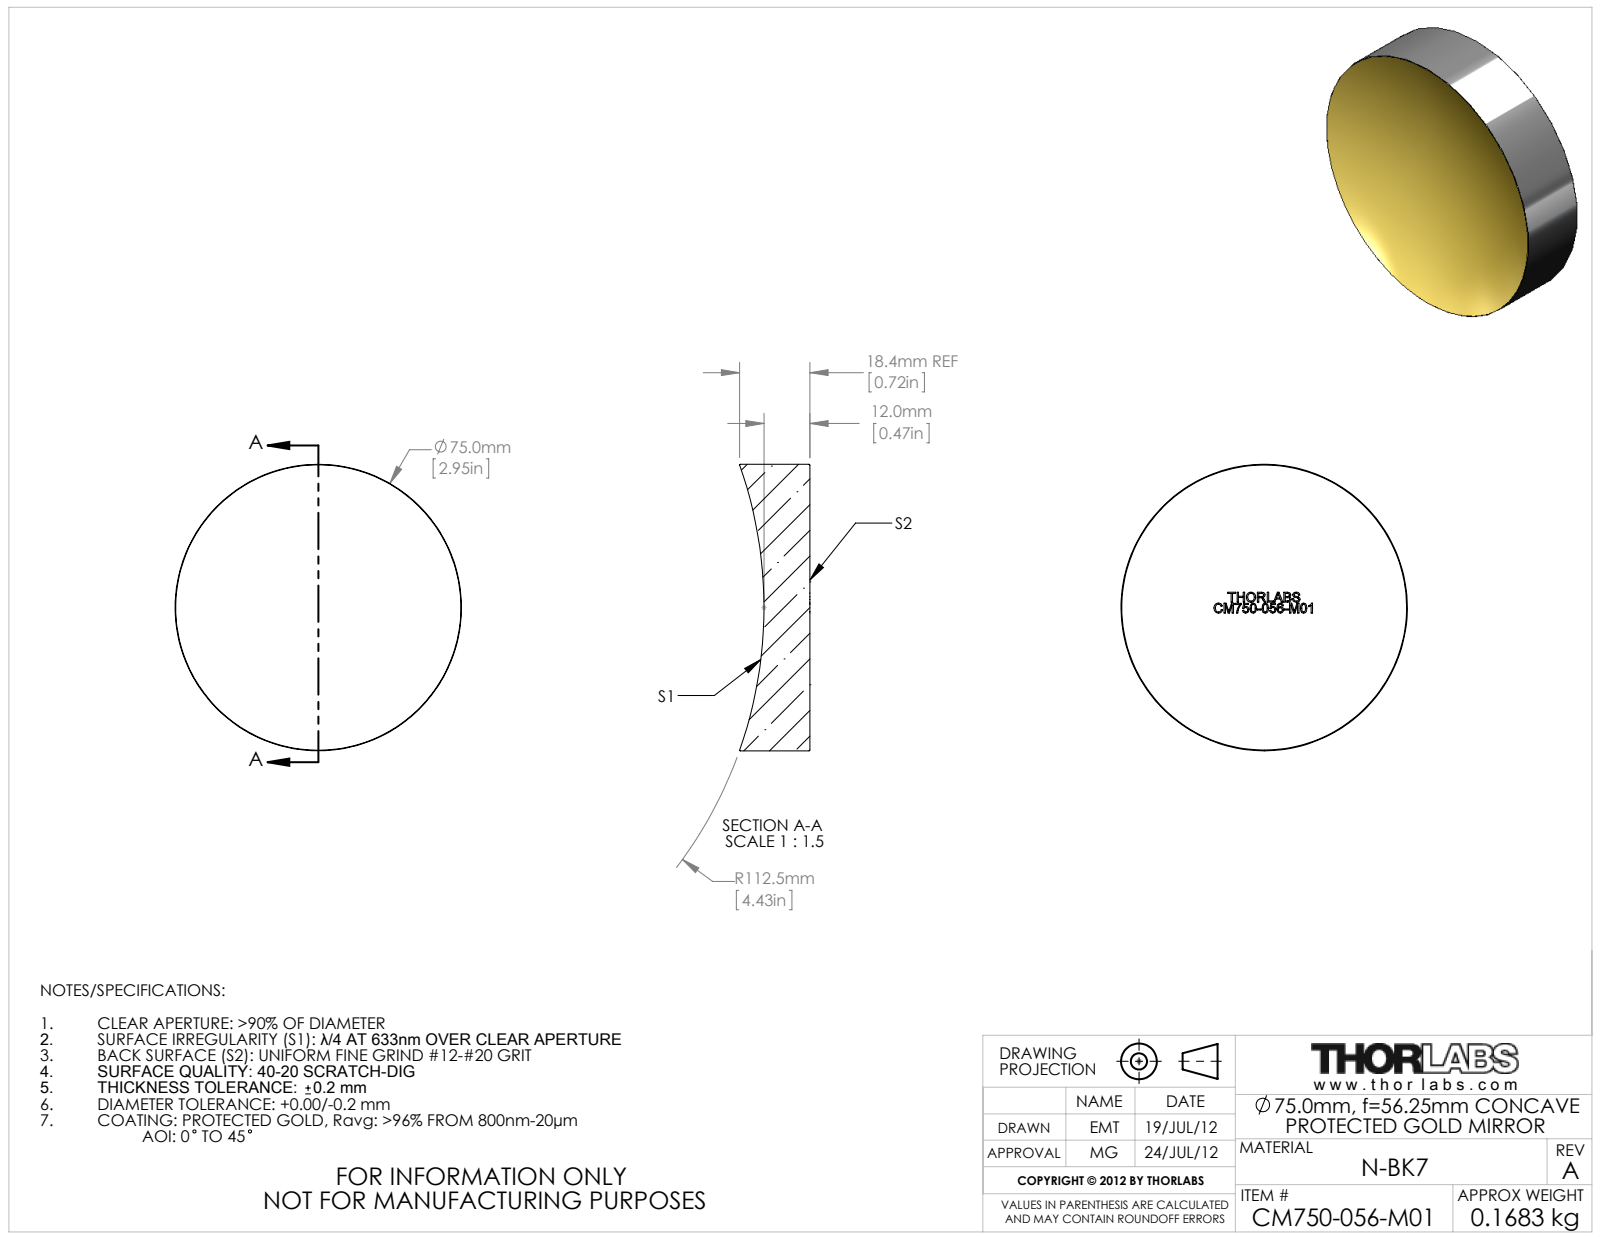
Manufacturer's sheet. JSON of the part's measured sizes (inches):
{"part_name": "24639-E0W", "step_written_by": "SolidWorks 2011 (CONFIG_CONTROL_DESIGN)", "units": "inches", "bodies": {"solids": 0, "faces": 39, "planar": 31, "cylindrical": 2, "other": 6}, "overall_size": [2.953, 2.953, 0.724], "round_bosses_or_shafts": [[2.953, 1]]}
